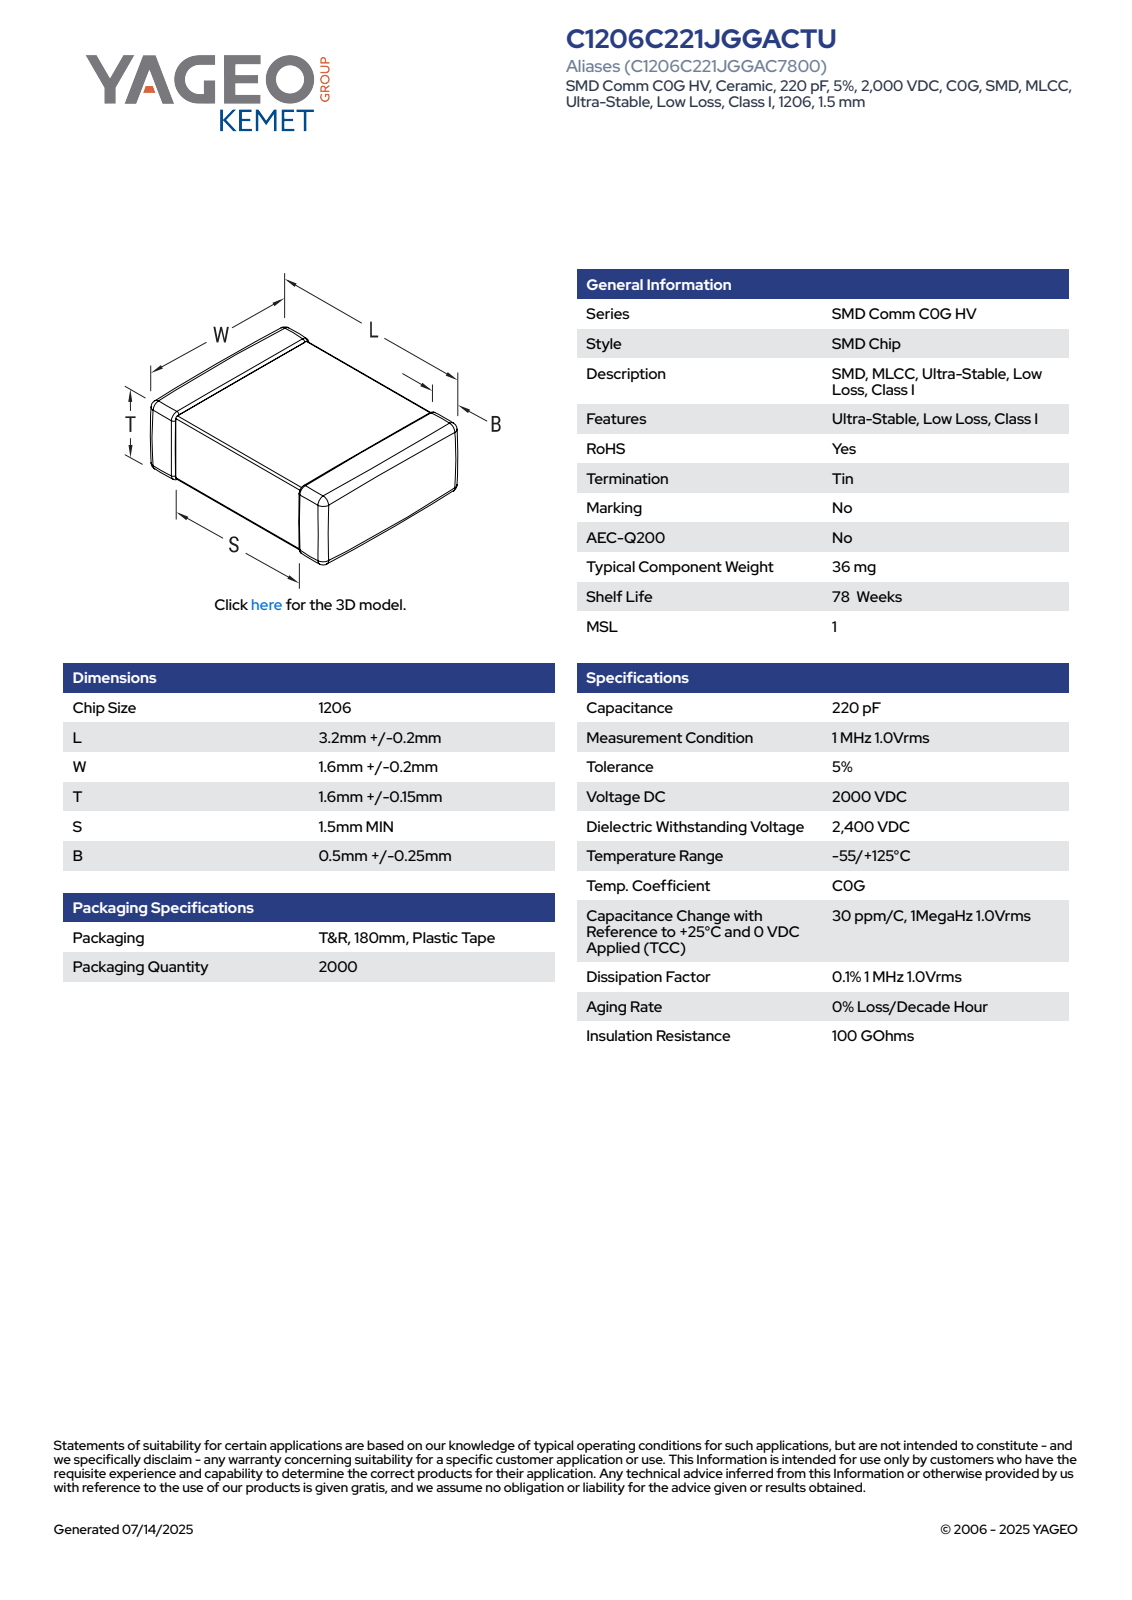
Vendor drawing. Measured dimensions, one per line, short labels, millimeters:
name: CCS_CCSTD_1206_L3.4W1.8T1.75B0.5
written by: SolidWorks 2021 (AUTOMOTIVE_DESIGN)
unit: mm
bodies: 4 solids, 125 faces (71 planar, 38 cylindrical, 16 other)
size: 3.4 × 1.8 × 1.75
volume: 10 mm³; area: 30 mm²
face distances: 1.71, 1.76, 1.72, 1.67, 3.4, 1.75, 1.8, 1.68, 1.57, 1.83
